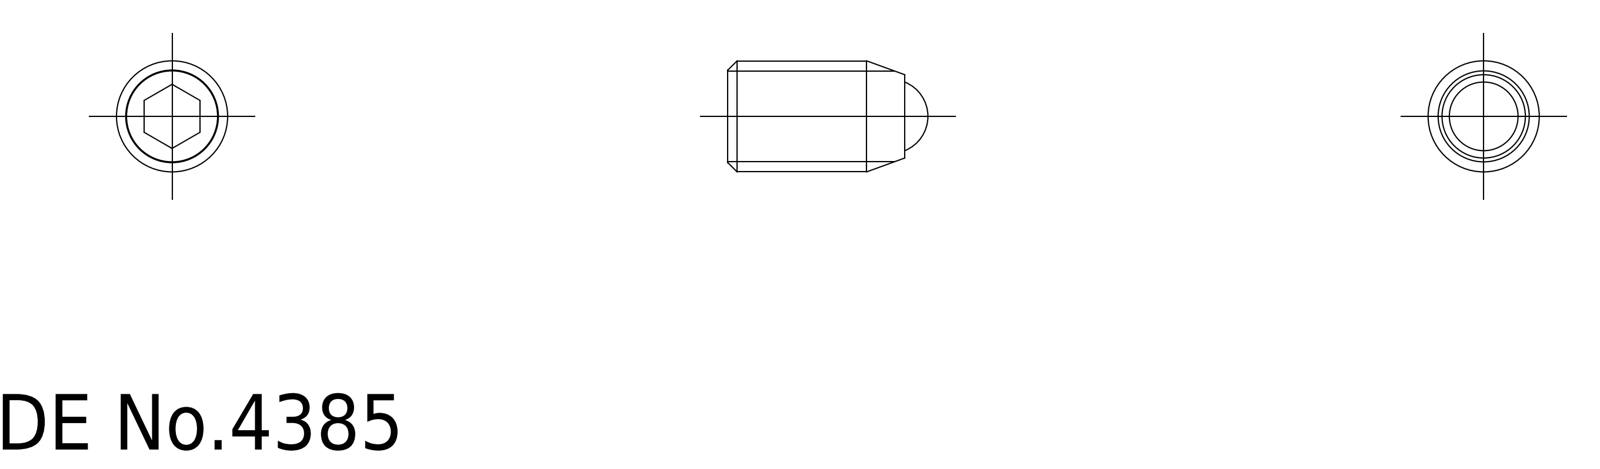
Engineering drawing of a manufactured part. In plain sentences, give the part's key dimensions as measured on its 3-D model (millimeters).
The part is named "ball; SCS_M6_10_R_17290_36". Its 3-D file was written by "CADfix (AUTOMOTIVE_DESIGN)". It is 2 solids with 20 faces: 0 planar, 0 cylindrical and 20 other. Overall it measures 10.8 by 6 by 6 millimeters. Its volume is 207 cubic millimeters and its surface area 358 square millimeters.
